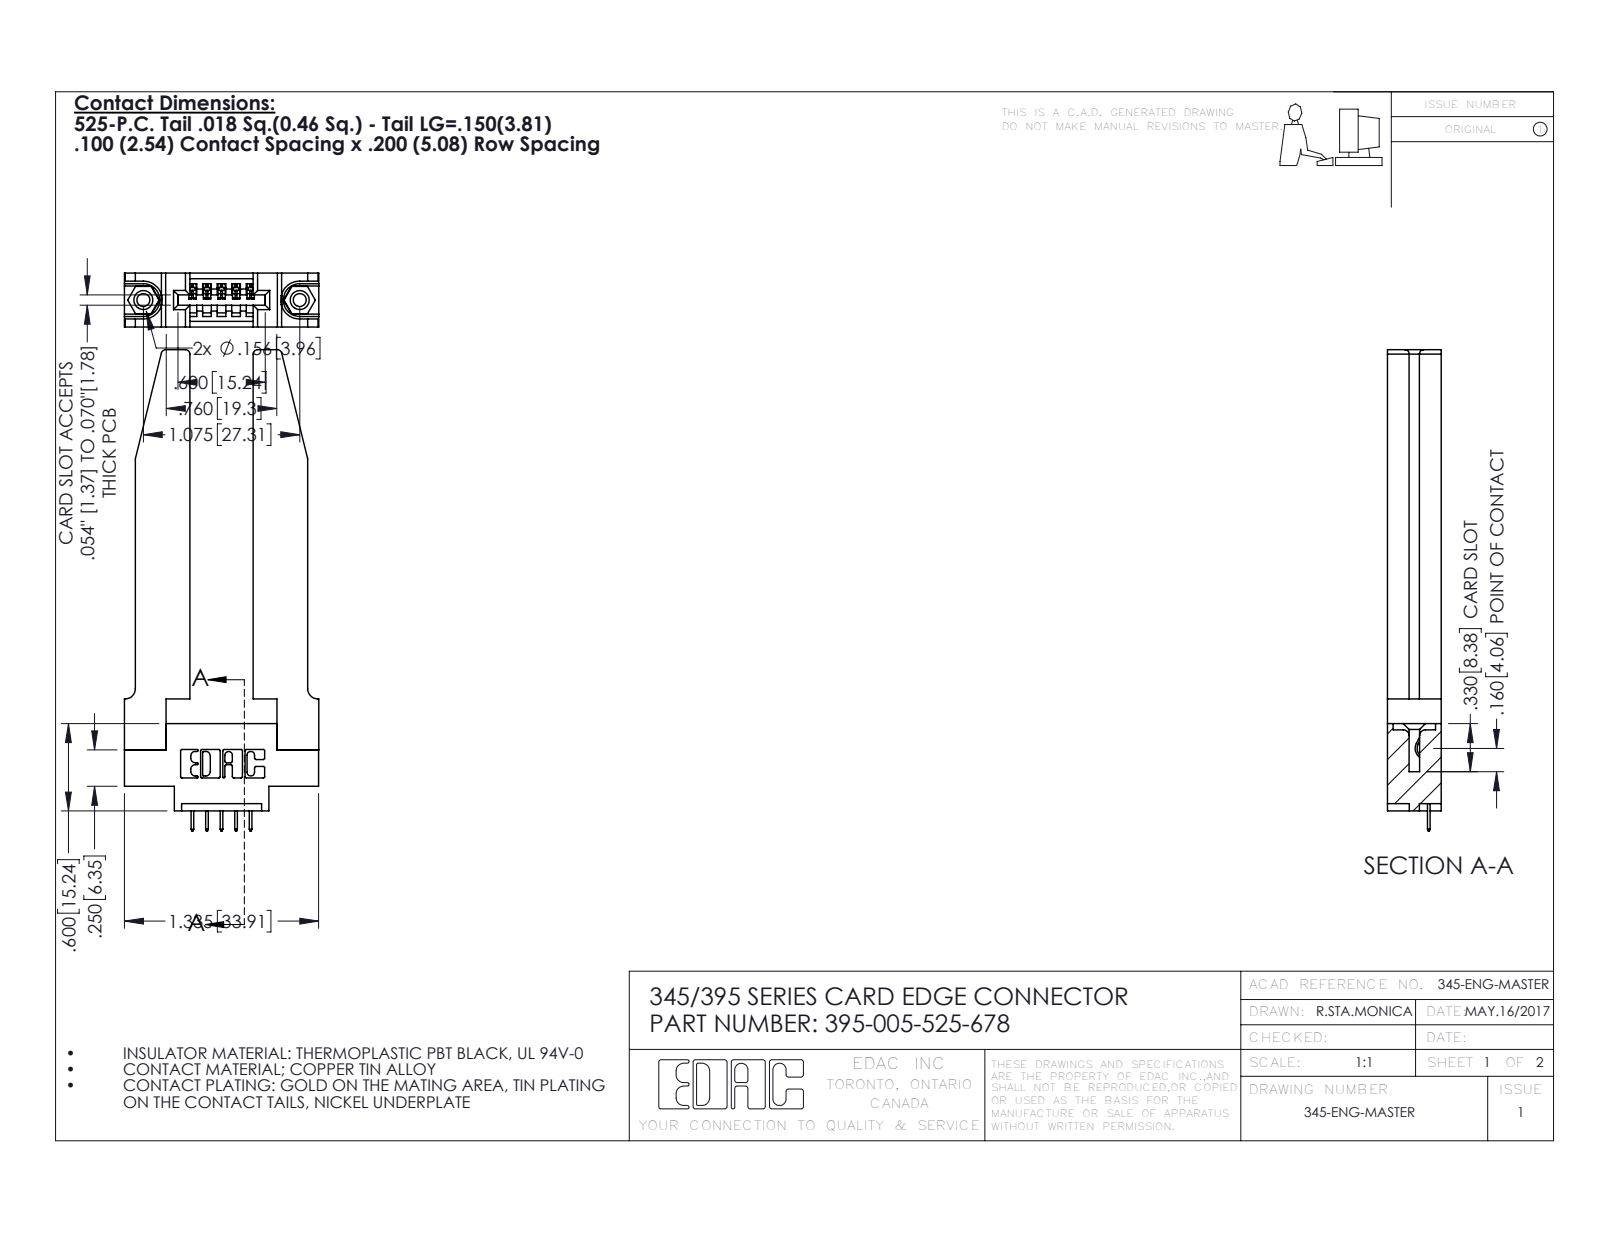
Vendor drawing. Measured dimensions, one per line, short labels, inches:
name: 345-292-001_345-293-125; 345-250-001_345-250-001-102; 345 Part_0.170 Offset - 0.156 Dia-TH; 395-005-525-678 (+1 more)
written by: SolidWorks 2020 (CONFIG_CONTROL_DESIGN)
unit: in
bodies: 10 solids, 674 faces (456 planar, 166 cylindrical, 52 other)
size: 3.307 × 1.336 × 0.37
volume: 0.644 in³; area: 15.66 in²
holes: 2× ⌀0.089, 2× ⌀0.125, 2× ⌀0.156, 1× ⌀0.064
bosses: 2× ⌀0.155
rounds: 22× R0.01, 10× R0.006, 8× R0.03, 6× R0.007, 6× R0.031, 3× R0.026, 2× R0.031, 2× R0.04
face distances: 0.37, 0.15, 0.22, 0.435, 0.148, 0.072, 0.095, 0.298, 0.077, 0.071
hole spacings: 0.27, 0.847, 1.075
